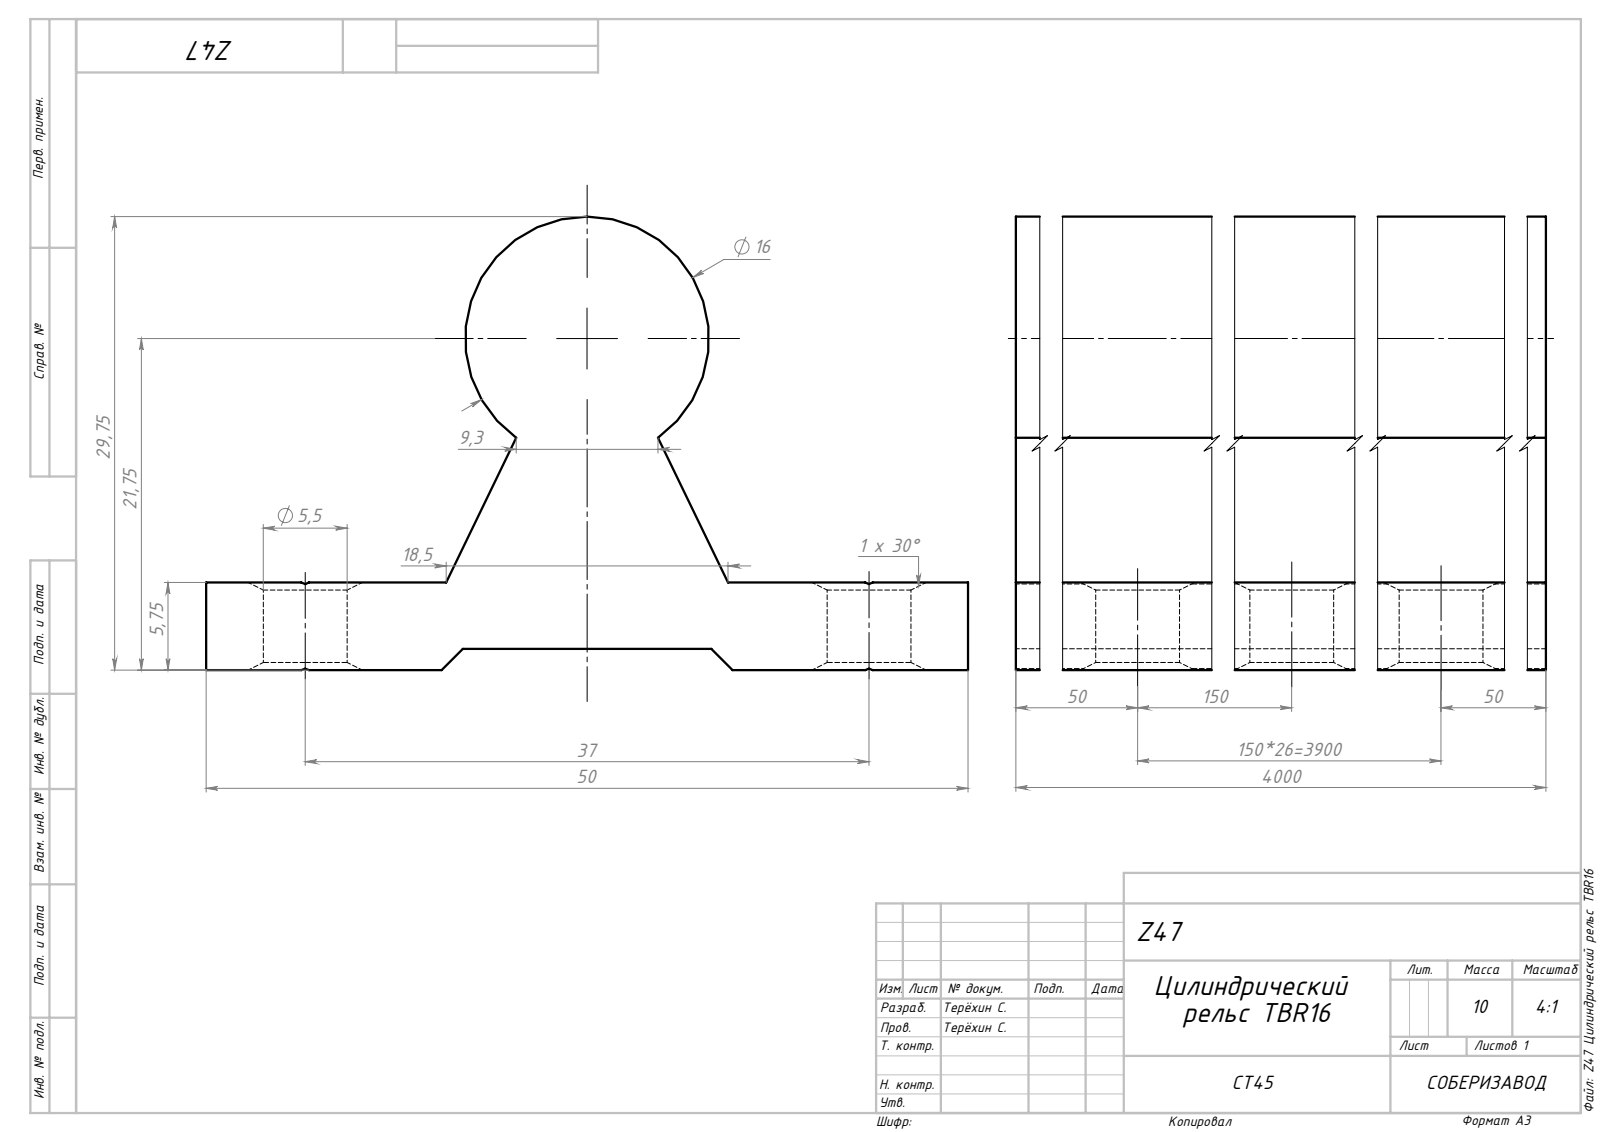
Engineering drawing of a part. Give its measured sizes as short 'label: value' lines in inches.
name: Сборка1; Z47 Цилиндрический рельс SBR16_00
written by: SolidWorks 2022 (AUTOMOTIVE_DESIGN)
unit: in
bodies: 1 solid, 568 faces (241 planar, 111 cylindrical, 216 other)
size: 157.48 × 1.969 × 1.171
volume: 142.6 in³; area: 970.7 in²
holes: 54× ⌀0.217
bosses: 1× ⌀0.63
face distances: 0.226, 0.055, 0.171, 1.969, 0.541, 0.203, 0.338, 0.743, 157.48
hole spacings: 5.906, 11.811, 17.717, 23.622, 29.528, 35.433, 41.339, 47.244
